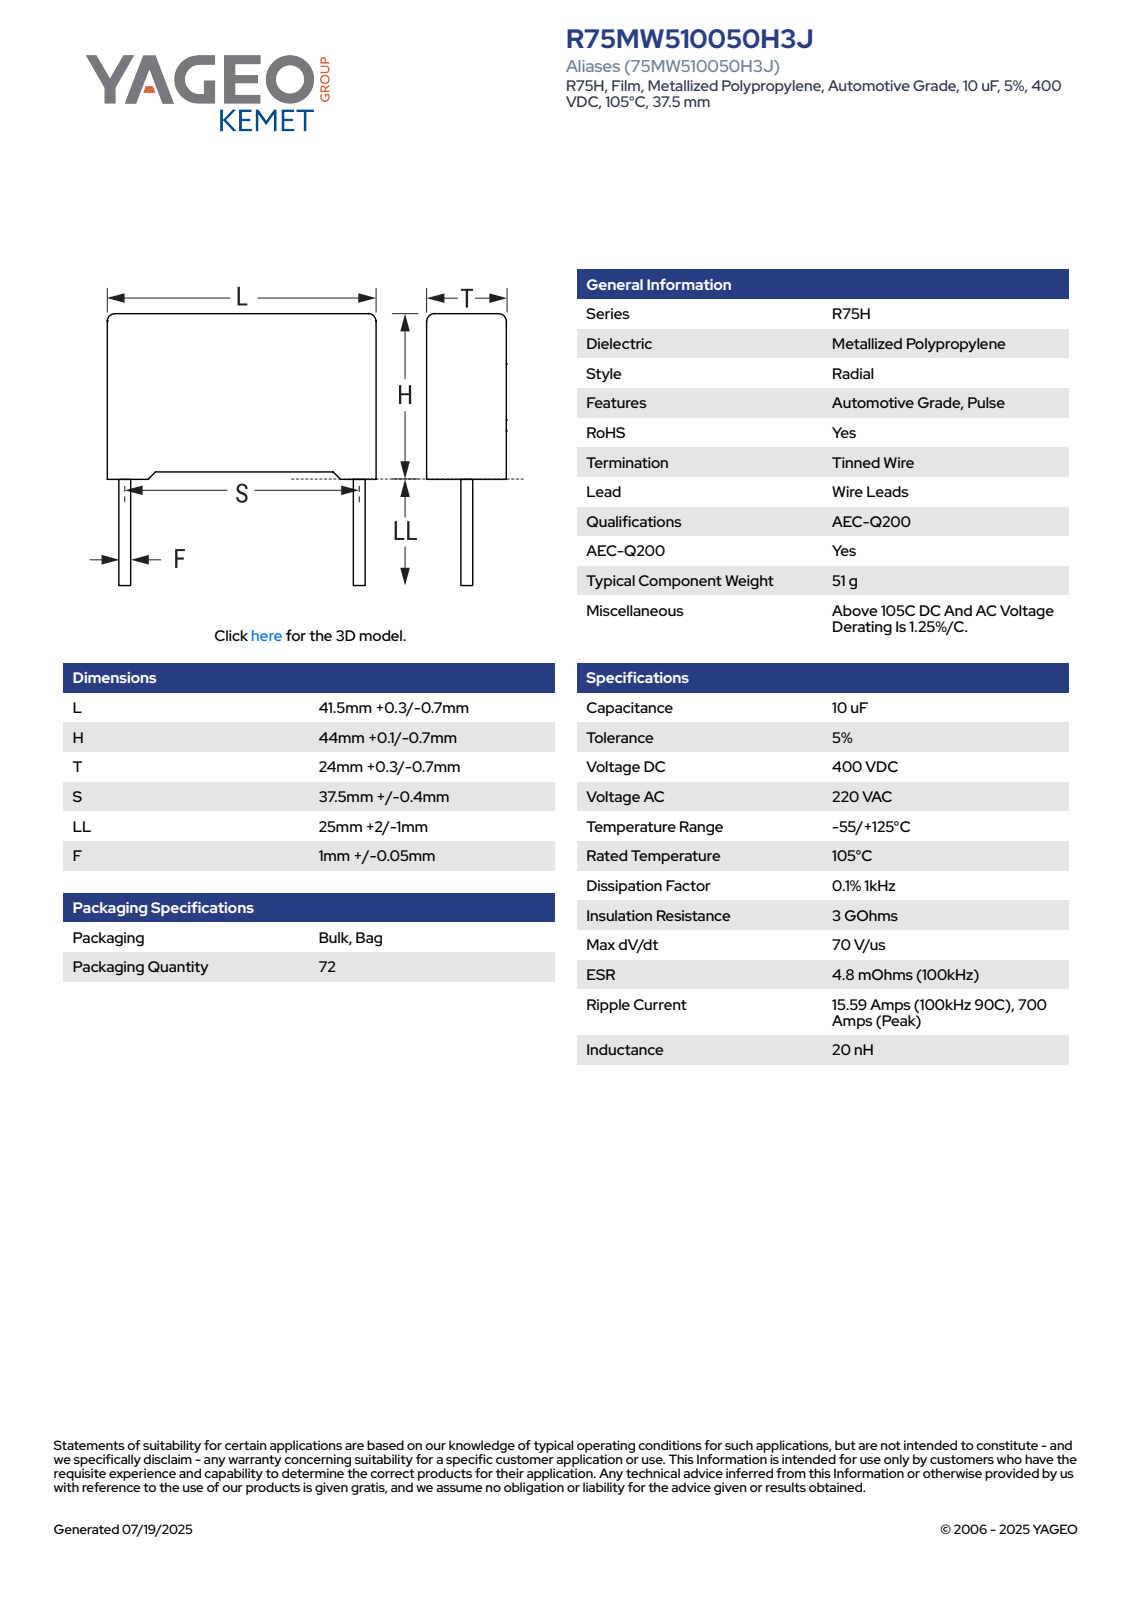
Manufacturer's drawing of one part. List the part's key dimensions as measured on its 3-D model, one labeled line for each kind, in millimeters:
Part name (STEP PRODUCT): CFR_RB2_41.5X44X24_L41.8H44.1T24.3S37.5LL27F1.05
STEP written by: SolidWorks 2021 (AUTOMOTIVE_DESIGN)
Units: millimetres
Bodies: 4 solids, 85 faces (77 planar, 8 cylindrical, 0 other)
Overall size (bounding box): 71.1 × 41.8 × 24.3
Volume: 43 522 mm³ · Surface area: 8 106 mm²
Round bosses / shafts (diameter × count): ⌀1.05 ×2
Partial cylindrical surfaces — rounded edges, fillets, slot ends (radius × count): R0.5 ×4
Main face-to-face distances: 24.3, 41.8, 42.58, 0.77, 43.35, 0.75, 1.52, 44.1, 1.39, 40.41
